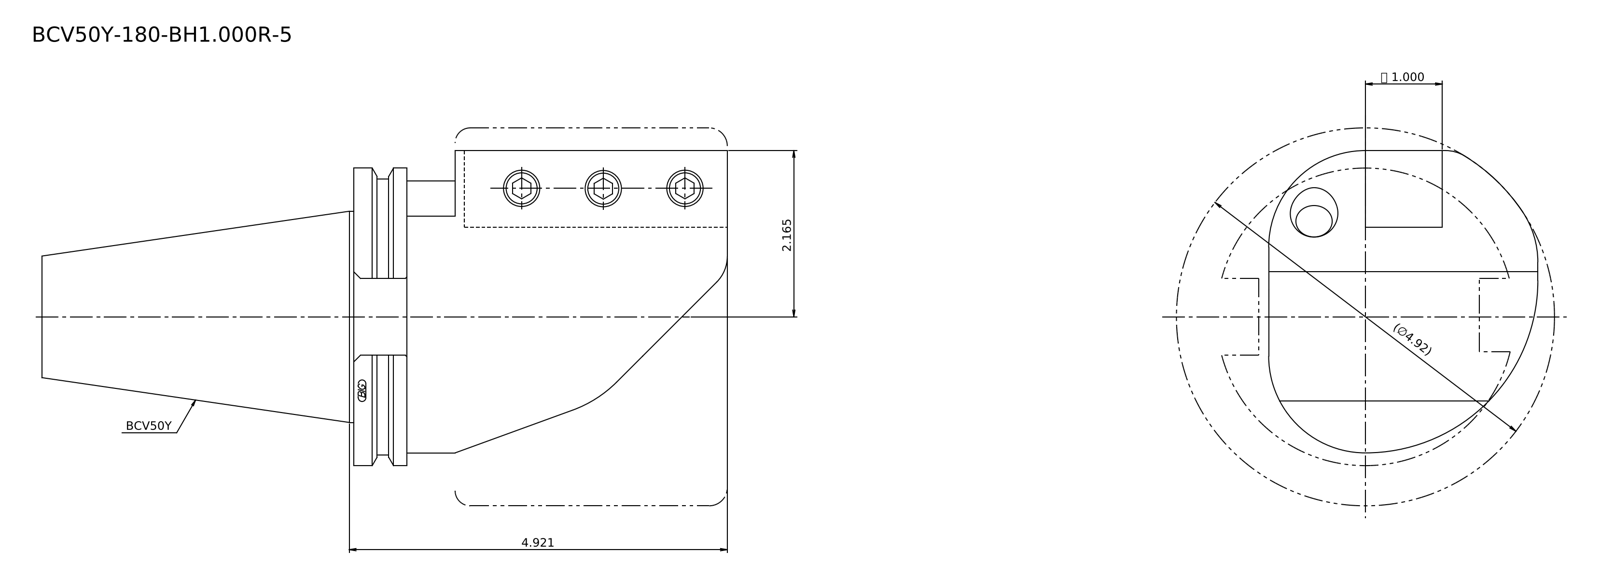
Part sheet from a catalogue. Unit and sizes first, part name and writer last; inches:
Units: inches
Overall size (bounding box): 8.921 × 4.181 × 4.103
Round bosses / shafts (diameter × count): ⌀3.875 ×1, ⌀3.594 ×1, ⌀2.75 ×1
Partial cylindrical surfaces — rounded edges, fillets, slot ends (radius × count): R1.26 ×2, R0.472 ×1, R1.181 ×1, R1.772 ×1, R2.244 ×1, R2.461 ×1
Main face-to-face distances: 1, 4.862, 1.26, 2.26, 4.171, 0.691, 3.543, 0.628, 1.319, 8.921
Volume: 58.6 in³ · Surface area: 112.6 in²
Bodies: 1 solid, 31 faces (16 planar, 11 cylindrical, 4 other)
STEP written by: Kubotek KeyCreator 2011 V10.0.2 (22737) (automotive_design)
